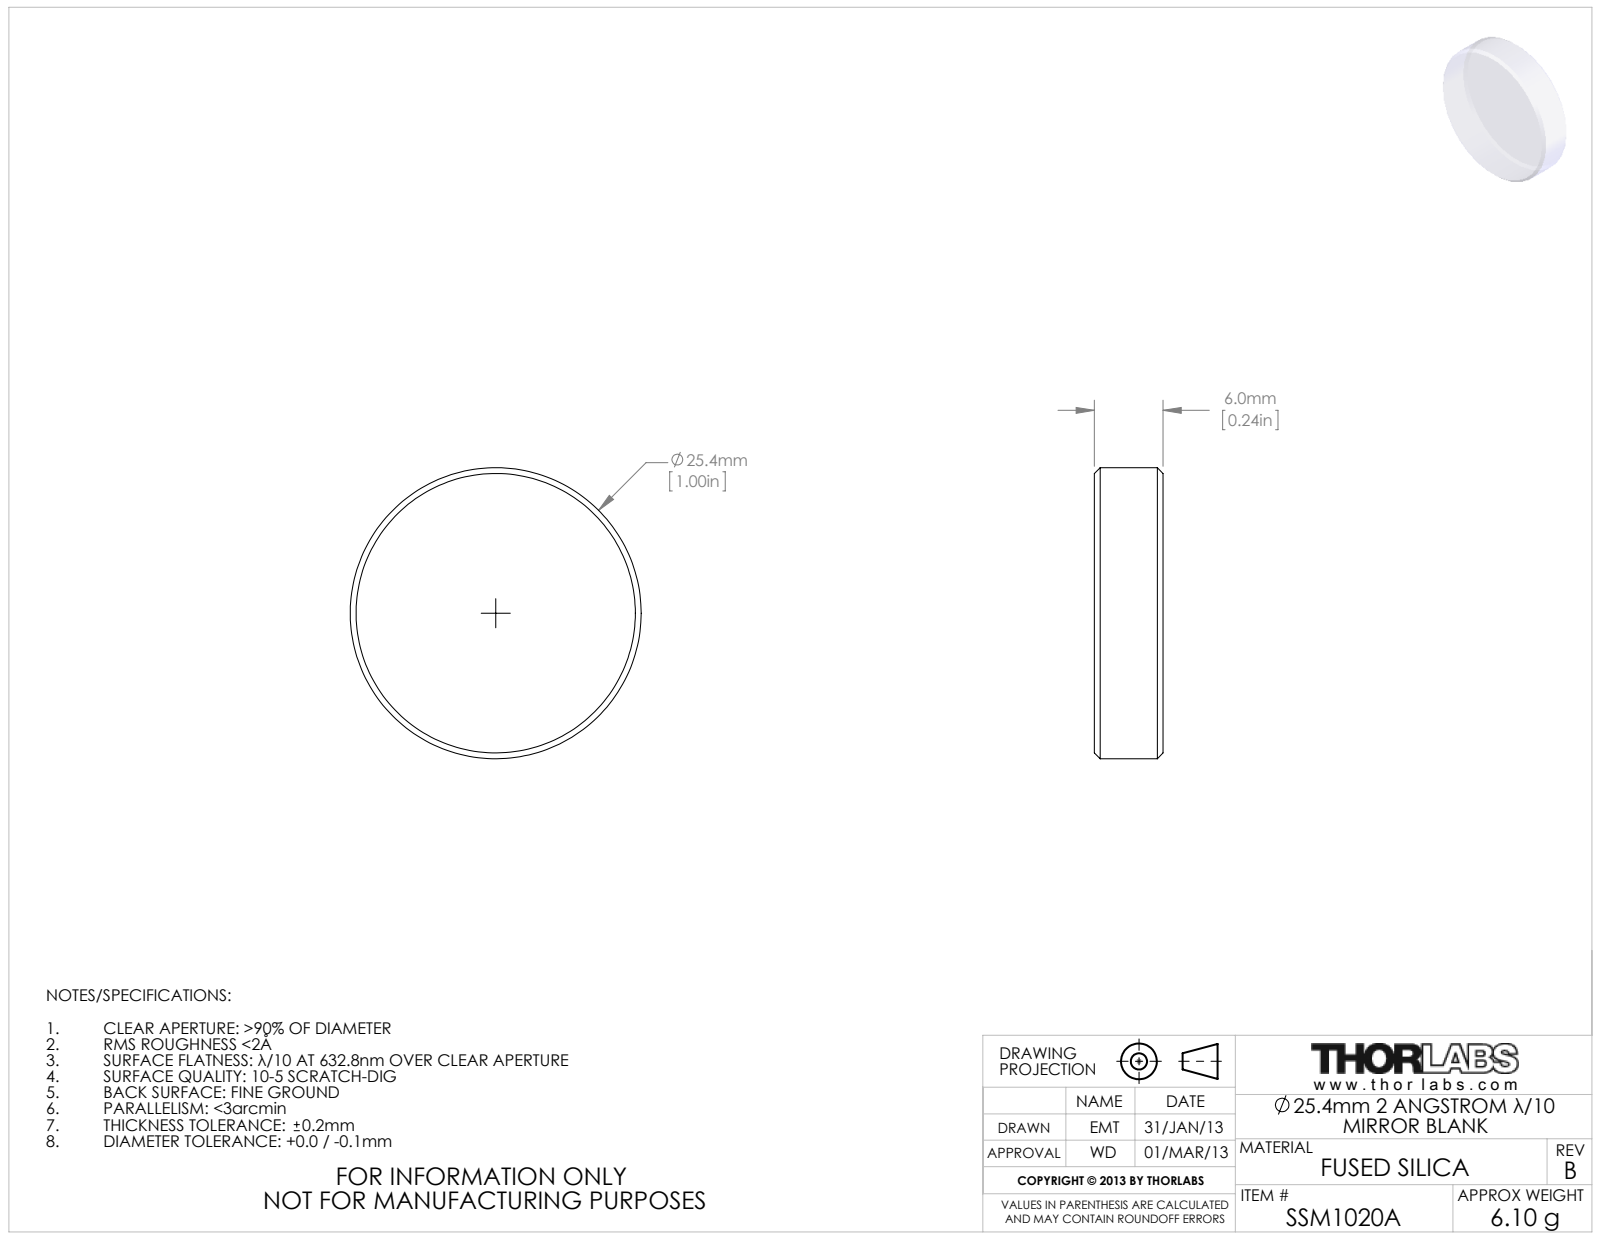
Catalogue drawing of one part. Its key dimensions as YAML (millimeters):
part_name: "TTN008869-E0W"
step_written_by: "SolidWorks 2012 (CONFIG_CONTROL_DESIGN)"
units: millimeters
bodies: {solids: 0, faces: 8, planar: 2, cylindrical: 2, other: 4}
overall_size: [25.4, 25.4, 6]
round_bosses_or_shafts:
  - {diameter: 25.4, count: 1}
face_to_face_distances: [6]
